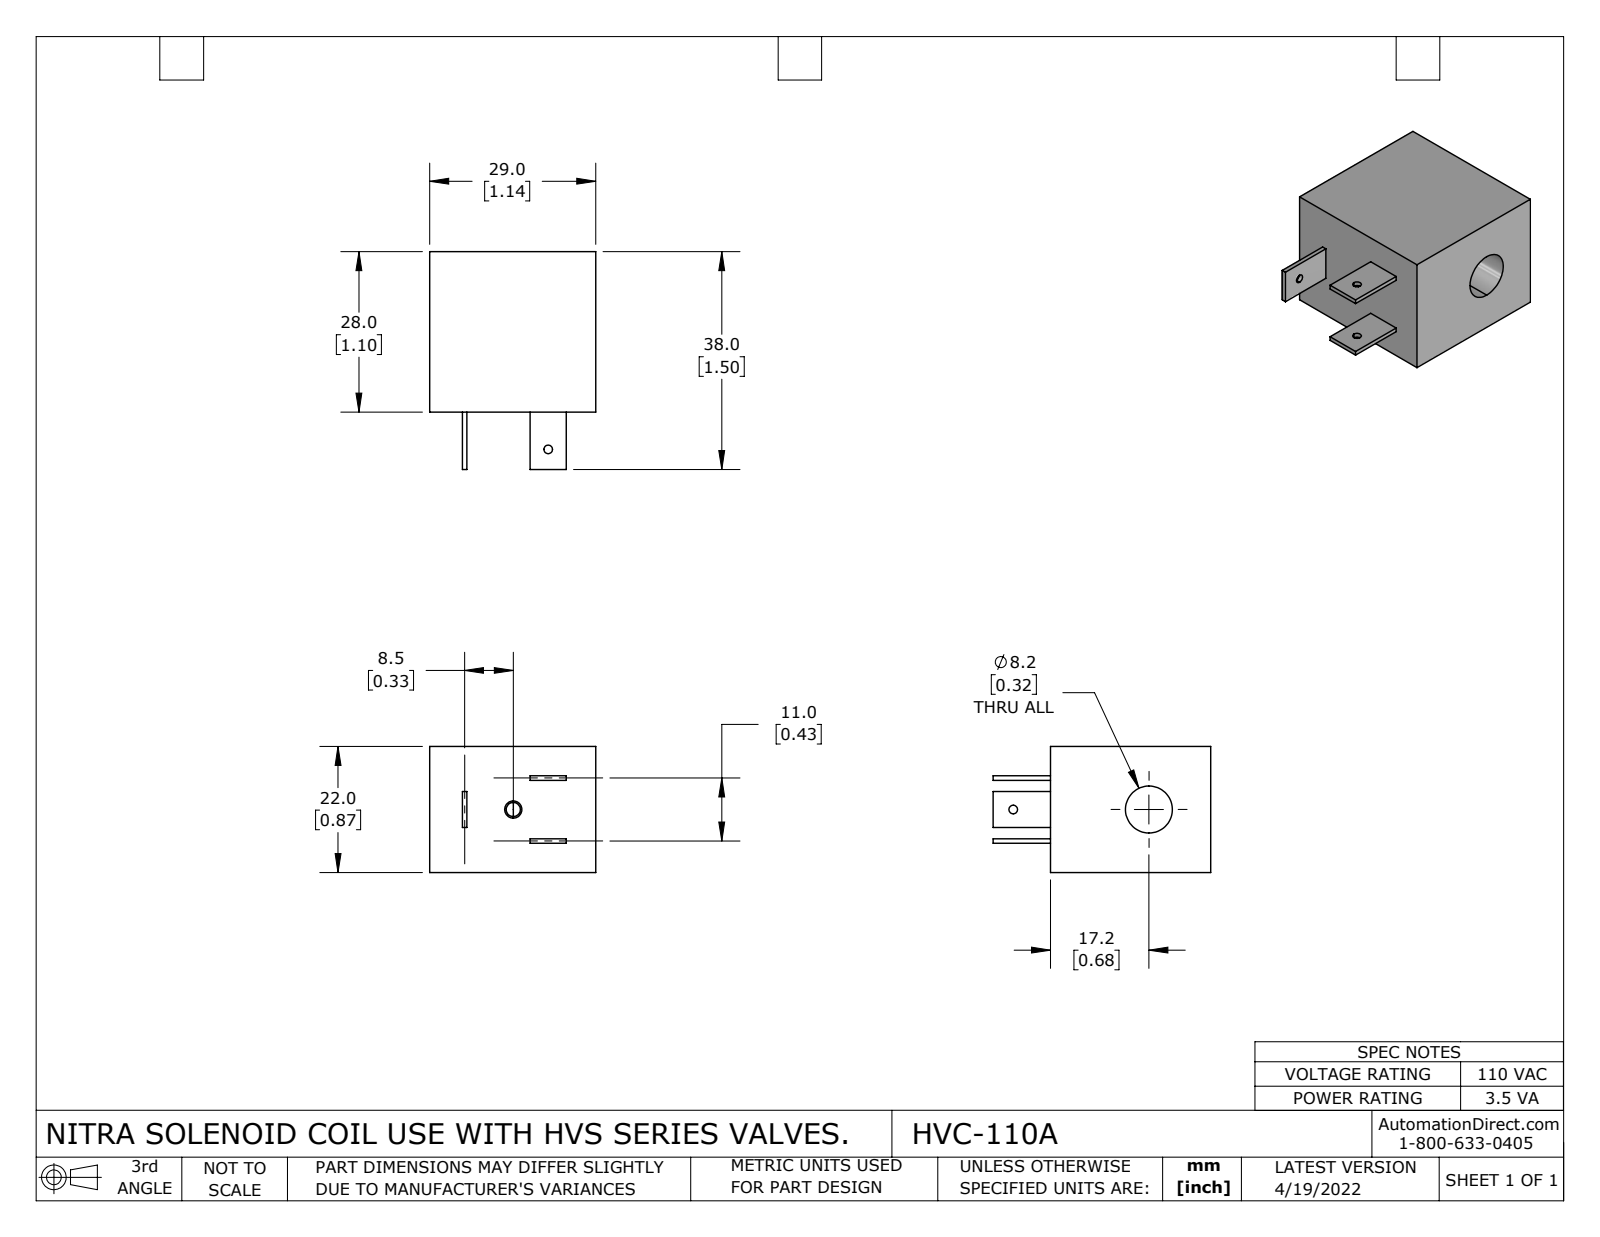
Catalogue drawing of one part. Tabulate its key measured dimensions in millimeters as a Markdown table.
| quantity | value |
| --- | --- |
| part name | HVC-110A |
| STEP written by | SolidWorks 2021 (CONFIG_CONTROL_DESIGN) |
| units | millimeters |
| bodies | 1 solid, 35 faces (21 planar, 10 cylindrical, 4 other) |
| overall size | 38 × 29 × 22 |
| volume | 16 454 mm³ |
| surface area | 5 238 mm² |
| round holes (diameter × count) | 1.5 × 2, 2.46 × 1, 8.2 × 1 |
| main face-to-face distances | 22, 28, 29, 0.8, 5.1, 5.9, 16.1, 16.9, 11, 5.7 |
| hole center spacings | 23.7 |
